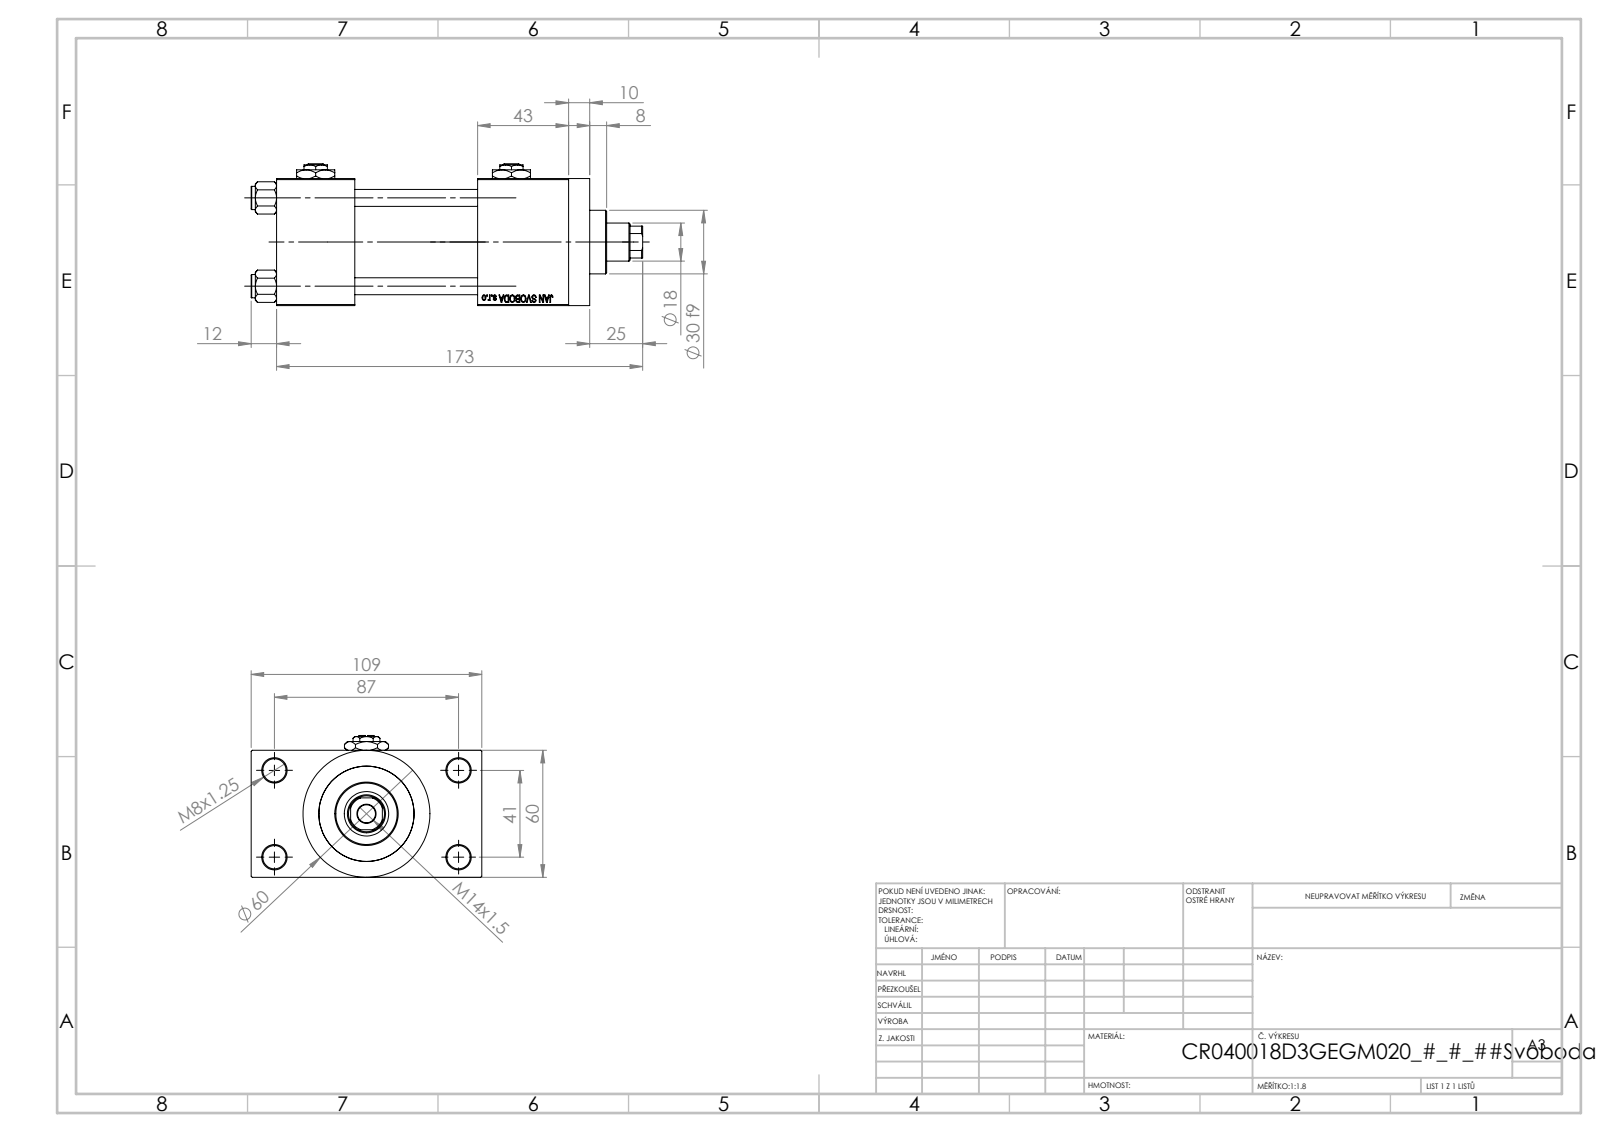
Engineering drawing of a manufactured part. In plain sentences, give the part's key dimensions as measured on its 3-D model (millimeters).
The part is named "V215CR_D_Body; NUT_M5_D; V215_VC_A; Zatka_pro_OIL_PORT (+2 more)". Its 3-D file was written by "SolidWorks 2019 (CONFIG_CONTROL_DESIGN)". It is 13 solids with 1206 faces: 546 planar, 100 cylindrical and 560 other. Overall it measures 185 by 109 by 67 millimeters. Its volume is 515 592 cubic millimeters and its surface area 123 915 square millimeters. Round holes: 4 of diameter 8, 4 of diameter 11, 2 of diameter 7, 2 of diameter 16.66, 2 of diameter 24, 1 of diameter 8.5, 1 of diameter 18, 1 of diameter 21, 1 of diameter 31, 1 of diameter 40, 1 of diameter 45. Round bosses or shafts: 4 of diameter 11, 1 of diameter 60, 1 of diameter 46, 1 of diameter 30. Partial cylindrical surfaces (rounded edges, fillets, slot ends): 1 of radius 8.5. The main face-to-face distances are 60, 24.5, 84.5, 58, 37, 95, 43, 138, 101, 109. The hole center spacings are 22.65, 29.49, 41.7, 47.15, 48.09, 64.35, 76.49, 41.
